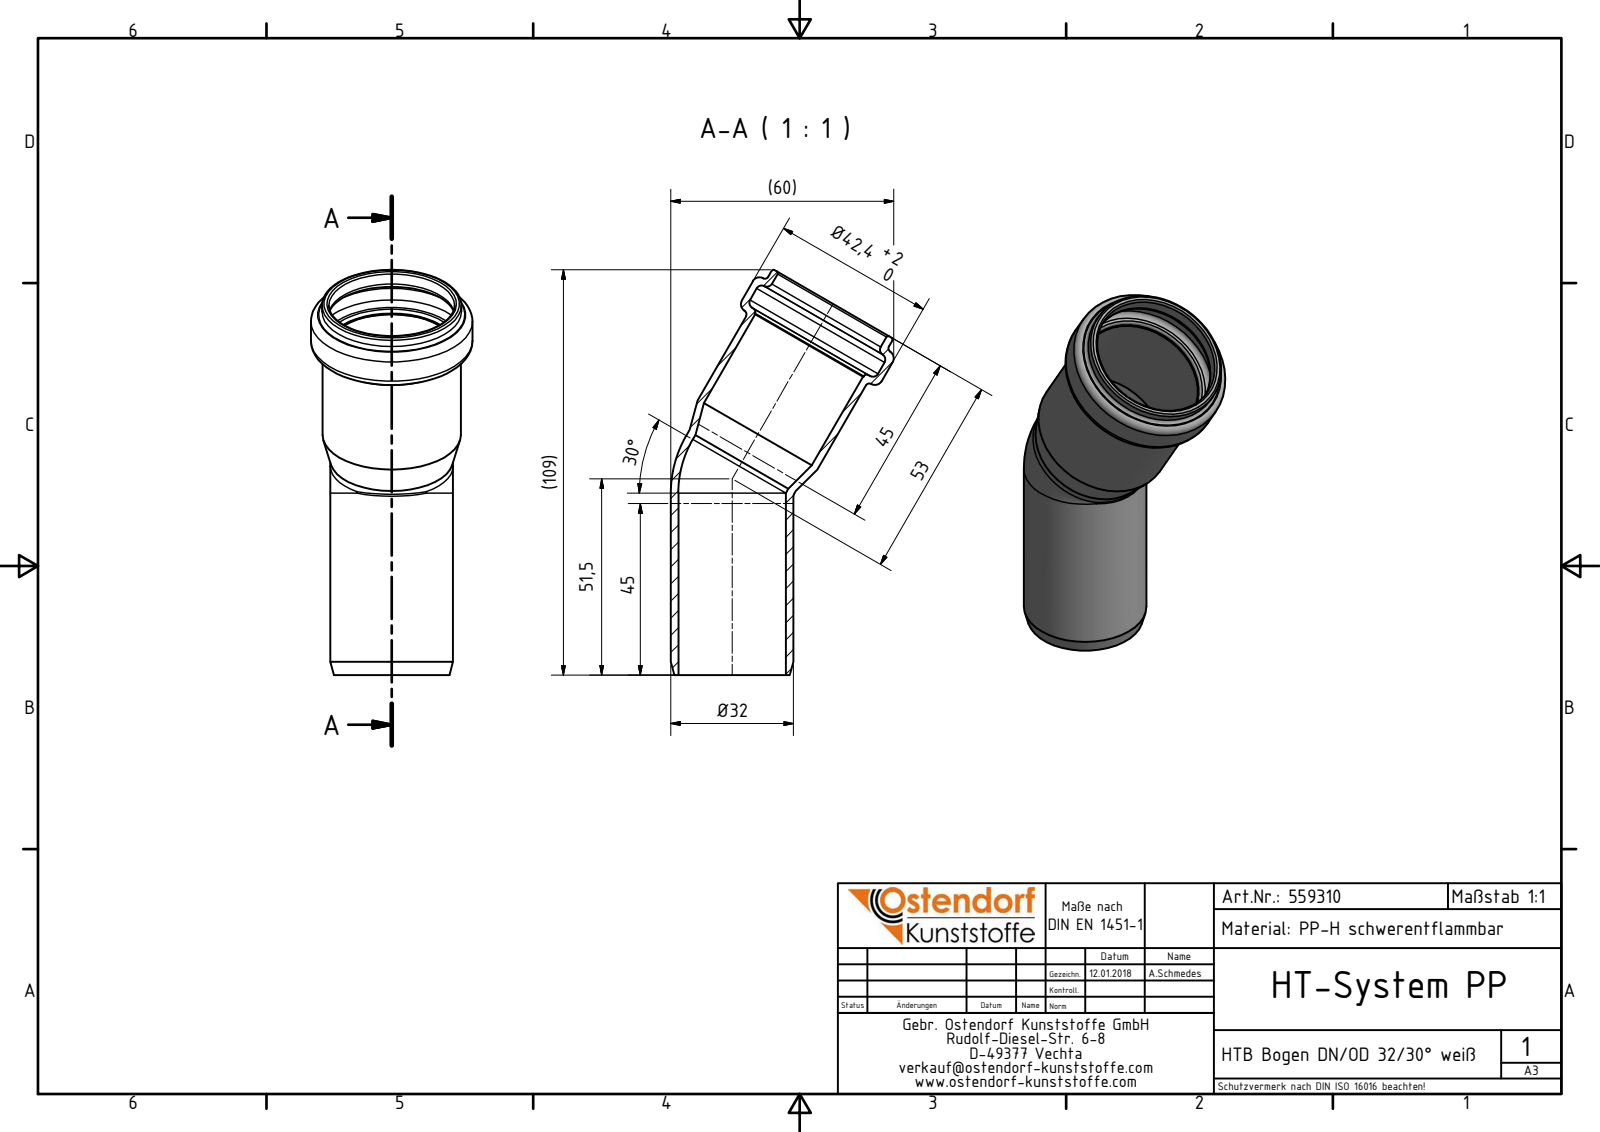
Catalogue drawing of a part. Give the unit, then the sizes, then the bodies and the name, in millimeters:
Units: millimetres
Overall size (bounding box): 106.37 × 58.55 × 42.4
Round holes (diameter × count): ⌀28.2 ×2, ⌀32.7 ×1, ⌀33 ×1, ⌀38.8 ×1
Round bosses / shafts (diameter × count): ⌀32.2 ×2, ⌀42.4 ×1, ⌀36.6 ×1, ⌀36.3 ×1
Main face-to-face distances: 12.63
Volume: 21 046 mm³ · Surface area: 22 413 mm²
Bodies: 1 solid, 34 faces (3 planar, 11 cylindrical, 20 other)
Part name (STEP PRODUCT): 559310 HTB DN_OD 32_30° weiß
STEP written by: Autodesk Inventor 2016 (AUTOMOTIVE_DESIGN)
